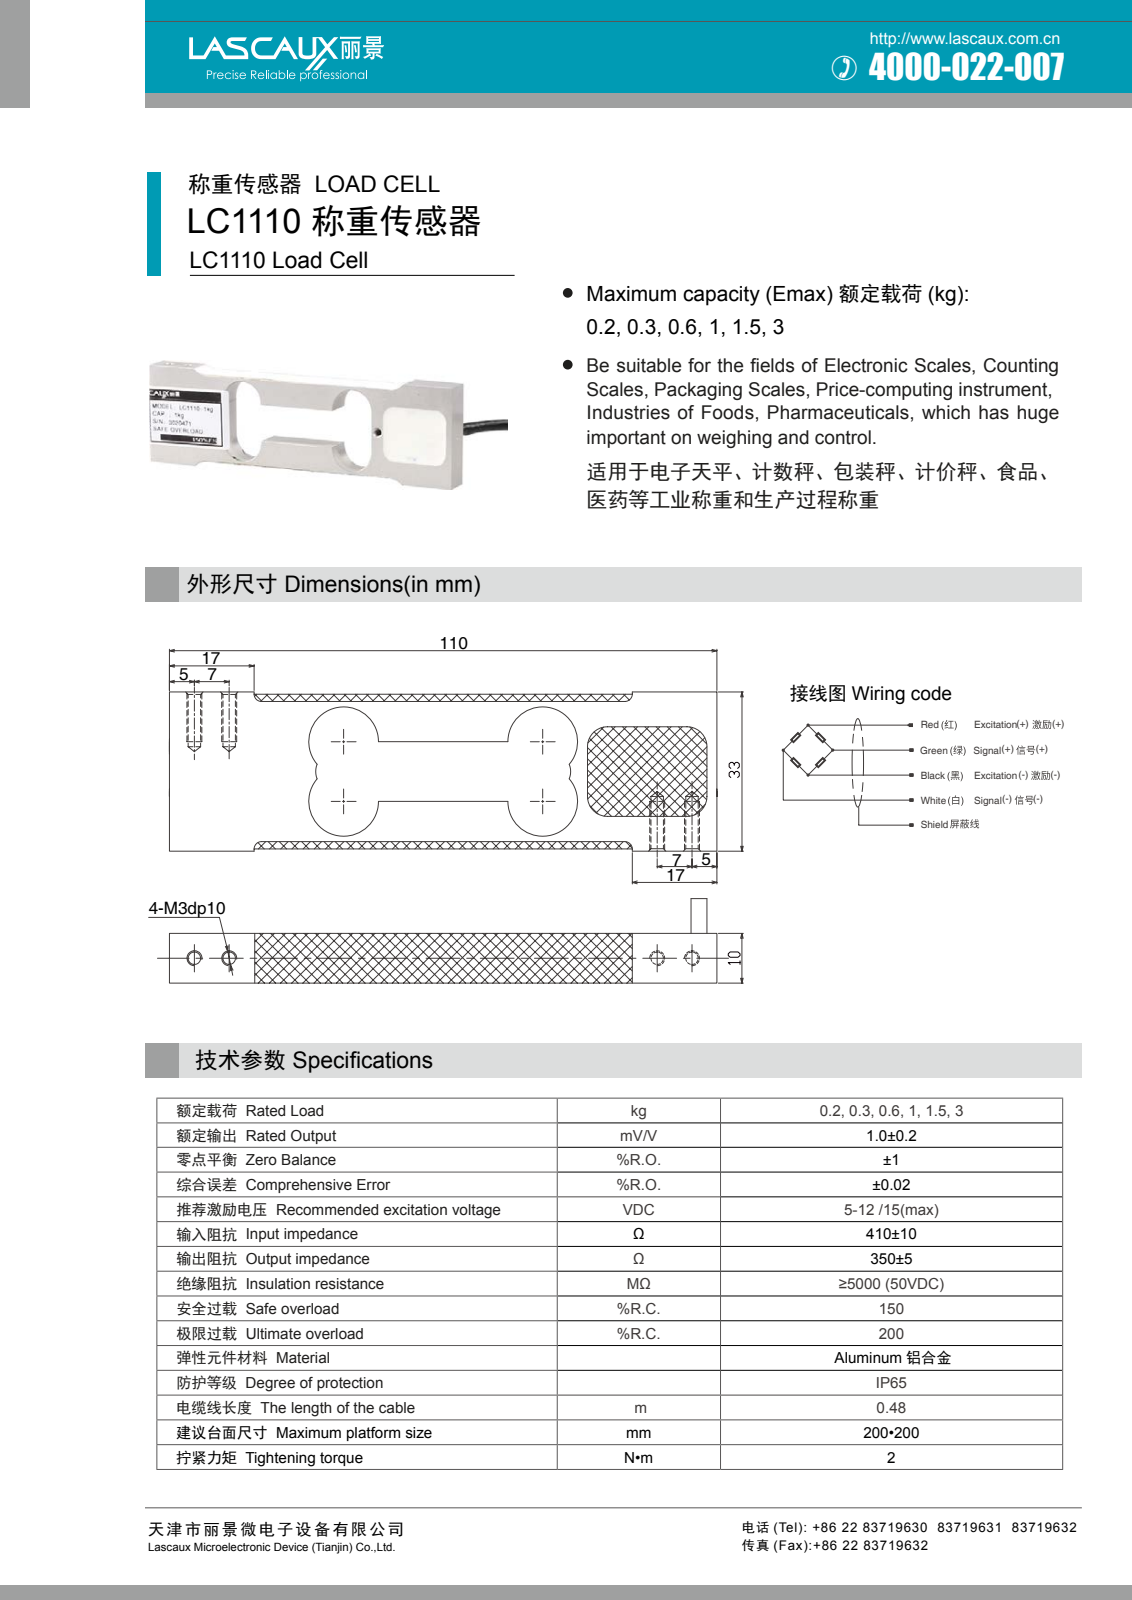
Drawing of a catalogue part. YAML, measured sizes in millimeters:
part_name: "LC1110"
step_written_by: "SolidWorks 2016 (CONFIG_CONTROL_DESIGN)"
units: millimeters
bodies: {solids: 1, faces: 42, planar: 18, cylindrical: 16, other: 8}
overall_size: [110, 33, 10]
volume: 22546
surface_area: 9430
round_holes:
  - {diameter: 2.5, count: 4}
partial_cylinders:
  - {radius: 1, count: 4}
  - {radius: 5, count: 4}
face_to_face_distances: [10, 7, 22, 29, 2, 9, 24, 31, 15, 33]
hole_center_spacings: [7, 93, 86, 100]
